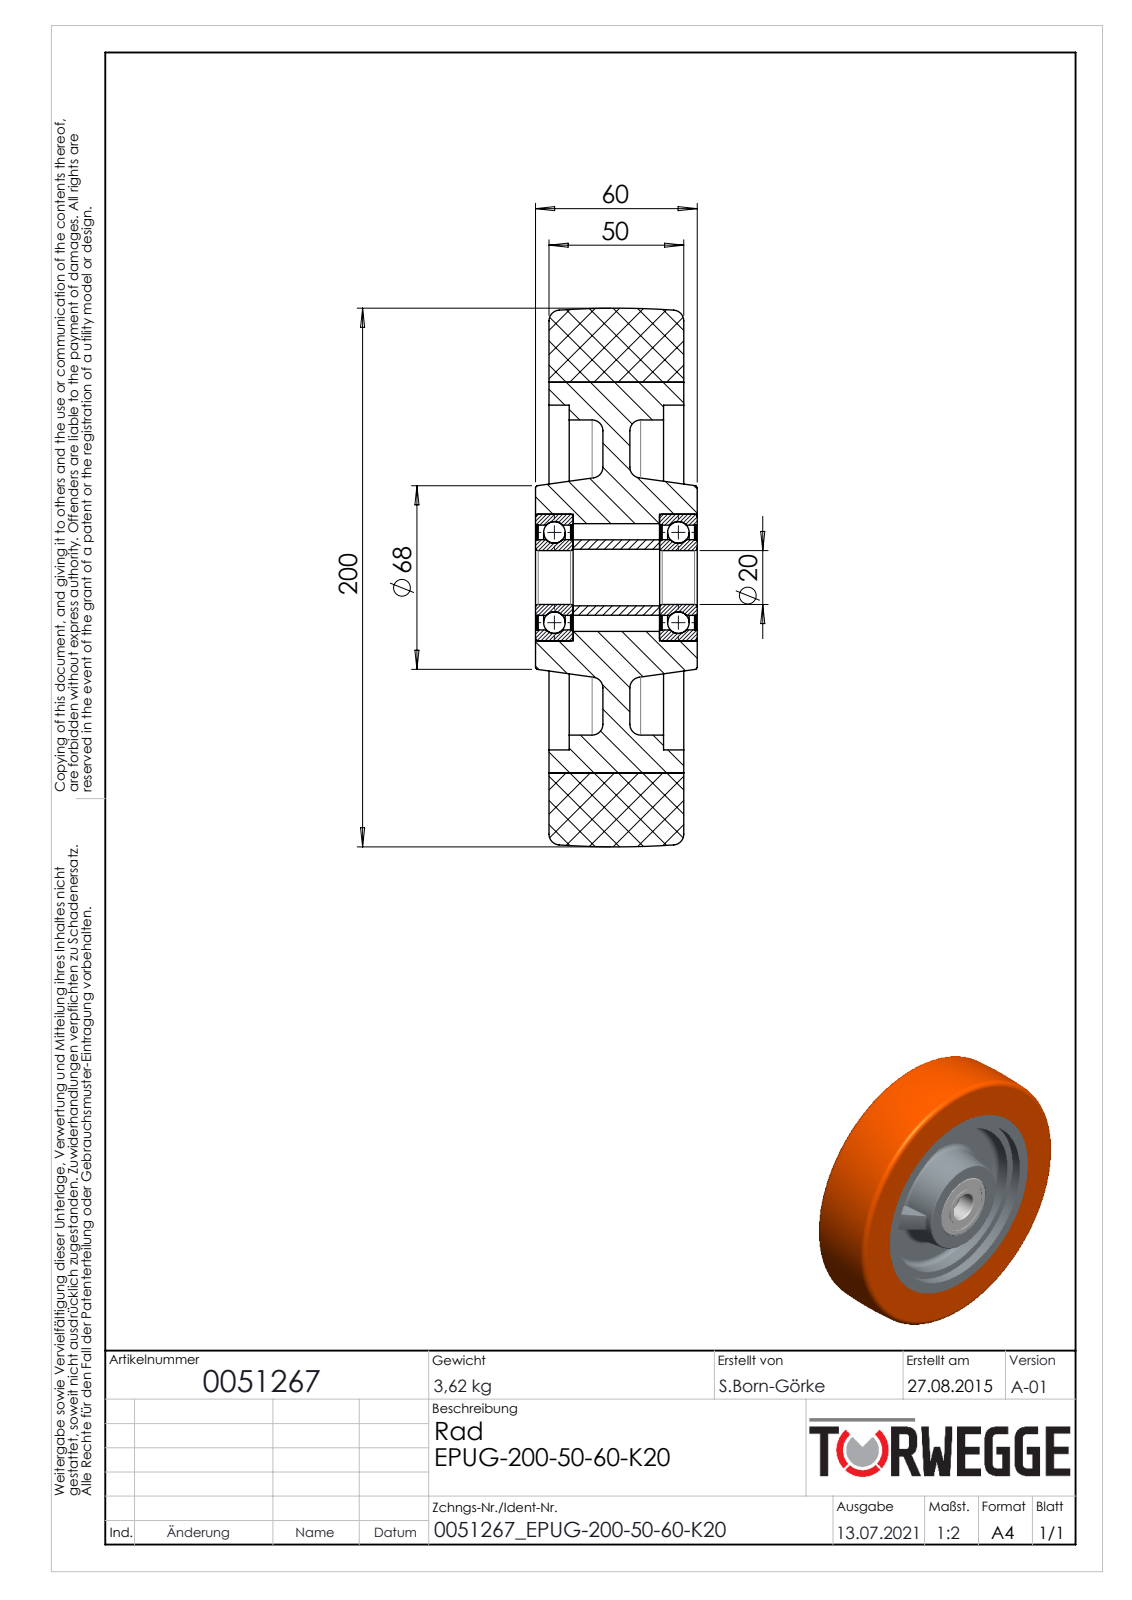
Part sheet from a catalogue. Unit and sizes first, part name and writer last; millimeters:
Units: millimetres
Overall size (bounding box): 200 × 200 × 60
Round holes (diameter × count): ⌀20 ×1, ⌀21 ×1, ⌀28.1 ×1, ⌀38.9 ×1, ⌀40 ×1, ⌀47 ×1, ⌀117 ×1, ⌀128 ×1, ⌀145 ×1
Round bosses / shafts (diameter × count): ⌀28 ×1
Partial cylindrical surfaces — rounded edges, fillets, slot ends (radius × count): R0.5 ×2
Main face-to-face distances: 50, 12.5, 20, 30, 35, 0.5, 5, 25, 55, 46
Volume: 1 254 000 mm³ · Surface area: 196 404 mm²
Bodies: 13 solids, 168 faces (32 planar, 64 cylindrical, 72 other)
Part name (STEP PRODUCT): 0051267
STEP written by: SolidWorks 2020 (AUTOMOTIVE_DESIGN)
